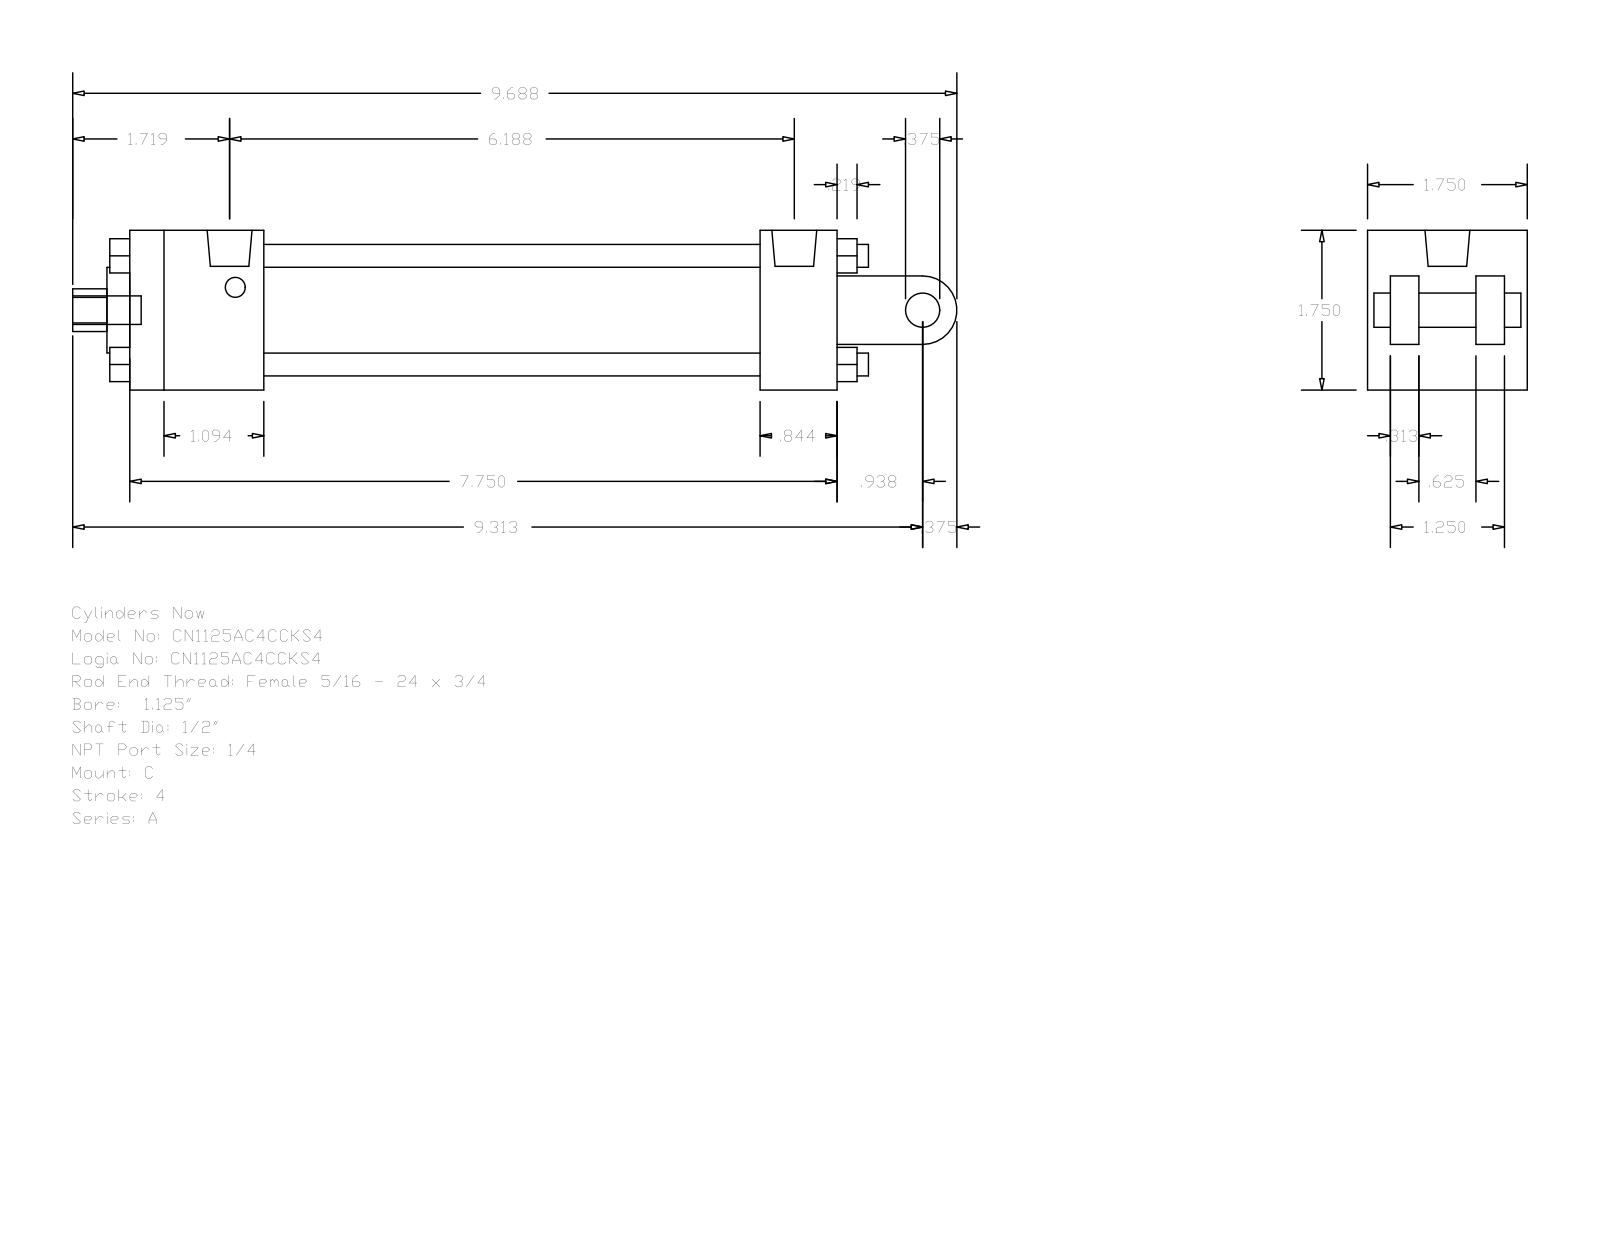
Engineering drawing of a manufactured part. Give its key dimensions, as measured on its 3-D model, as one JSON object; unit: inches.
{"part_name": "A_C__0112_0.5", "step_written_by": "GSSL Pune (CONFIG_CONTROL_DESIGN)", "units": "inches", "bodies": {"solids": 0, "faces": 135, "planar": 102, "cylindrical": 33, "other": 0}, "overall_size": [9.687, 1.75, 1.75], "round_holes": [[0.219, 2], [0.492, 1], [0.5, 1], [0.937, 1], [1.255, 1]], "round_bosses_or_shafts": [[0.25, 4], [0.219, 2], [0.492, 1], [0.375, 1], [0.313, 1]], "partial_cylinders_radius": [[0.234, 1], [0.375, 1]], "face_to_face_distances": [1.75, 0.25, 1.25, 0.563, 7.75, 1.188, 6.906, 0.844, 1.469, 5.437], "hole_center_spacings": [0.063]}
